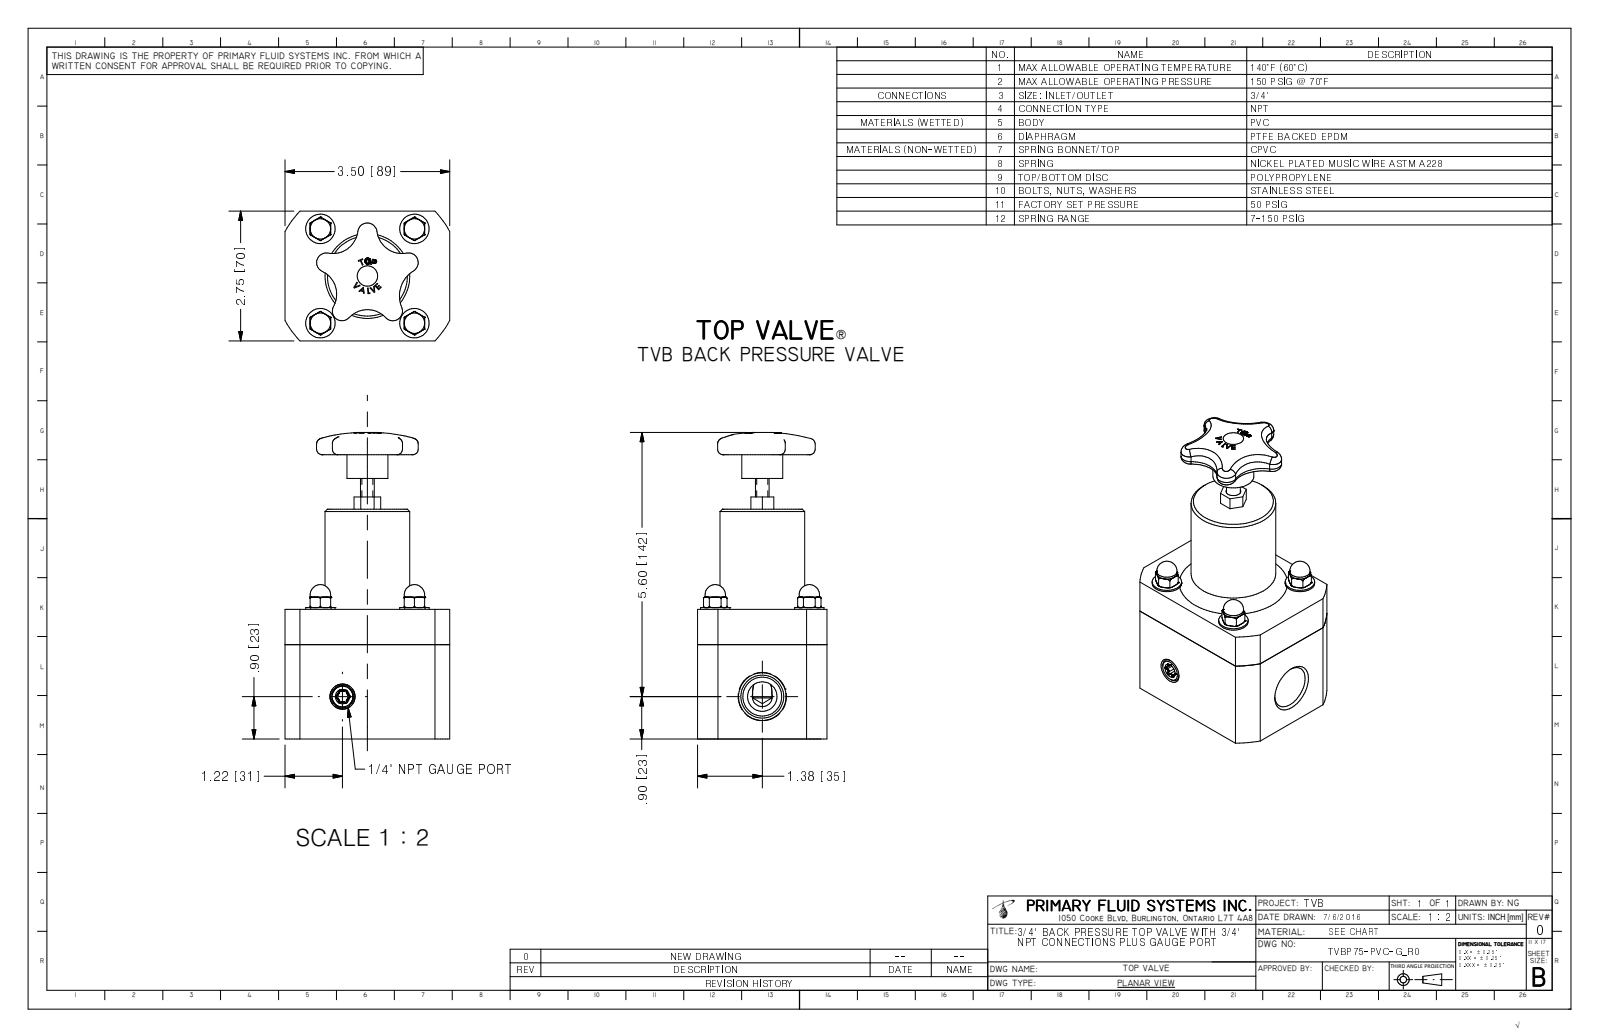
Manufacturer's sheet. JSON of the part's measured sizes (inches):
{"part_name": "TVBP75-PVC-G_R0", "step_written_by": "Autodesk Inventor 2009 (AUTOMOTIVE_DESIGN)", "units": "inches", "bodies": {"solids": 1, "faces": 361, "planar": 153, "cylindrical": 52, "other": 156}, "overall_size": [6.502, 3.5, 2.75], "volume_in3": 31.74, "surface_area_in2": 83.12, "round_holes": [[0.175, 4], [0.313, 1], [0.911, 1]], "round_bosses_or_shafts": [[0.625, 4], [0.433, 4], [0.375, 4], [1.8, 1], [0.87, 1], [0.293, 1]], "partial_cylinders_radius": [[0.027, 6], [0.085, 5], [0.205, 5], [0.536, 4], [0.656, 4], [0.625, 1], [0.745, 1], [1.988, 1]], "face_to_face_distances": [2.75, 2.75, 3.5, 4.875, 2.125, 0.75, 2, 0.433, 2.786, 0.036], "hole_center_spacings": [1.414, 2, 2.828]}
